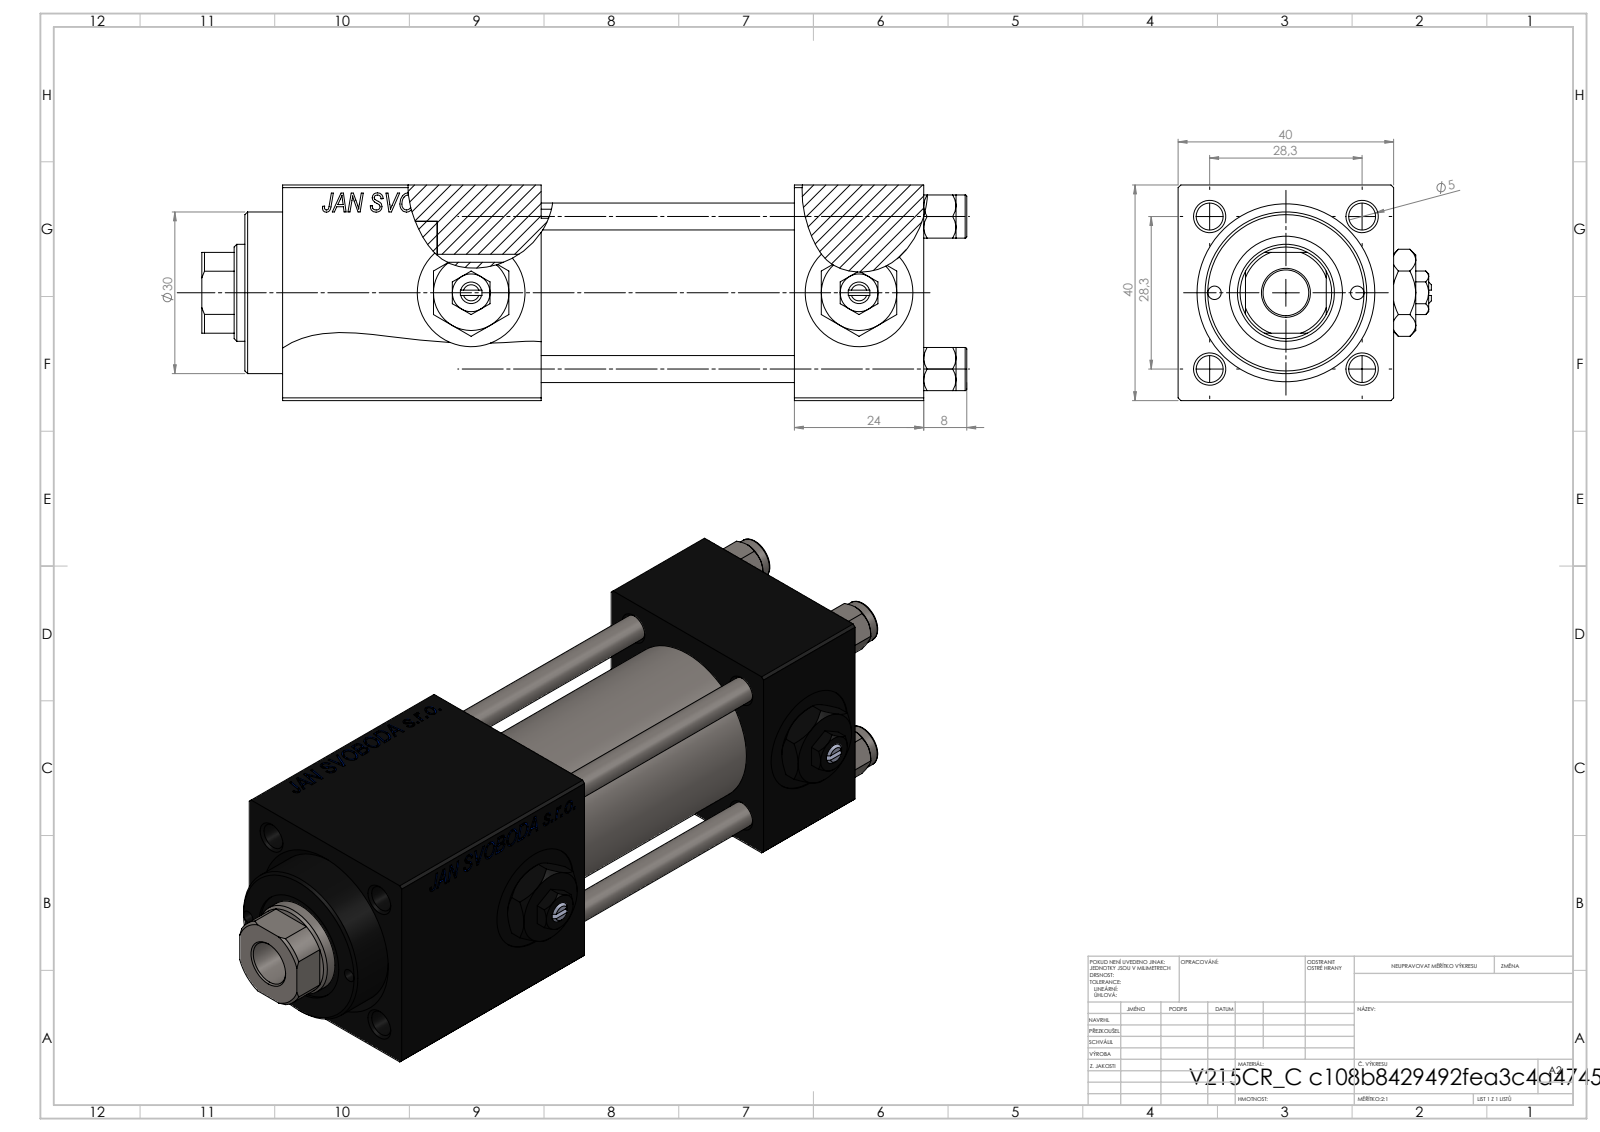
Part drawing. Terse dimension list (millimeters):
name: Zatka_pro_OIL_PORT; NUT_M5_C; V215CR_VCP_C; V215CR_C_TYCINKA (+2 more)
written by: SolidWorks 2019 (CONFIG_CONTROL_DESIGN)
unit: mm
bodies: 13 solids, 1251 faces (573 planar, 100 cylindrical, 578 other)
size: 142 × 47 × 40
volume: 148 475 mm³; area: 58 673 mm²
holes: 4× ⌀5, 3× ⌀20, 2× ⌀2.5, 2× ⌀7, 2× ⌀13.16, 1× ⌀8.5, 1× ⌀18, 1× ⌀21, 1× ⌀25, 1× ⌀30
bosses: 4× ⌀8, 1× ⌀31
rounds: 1× R8.5
face distances: 40, 24, 39.8, 47, 71, 90.3, 66.3, 19.3, 48, 95
hole spacings: 14.18, 20.01, 28.3, 30.84, 13.25, 40.02, 26.5, 72
